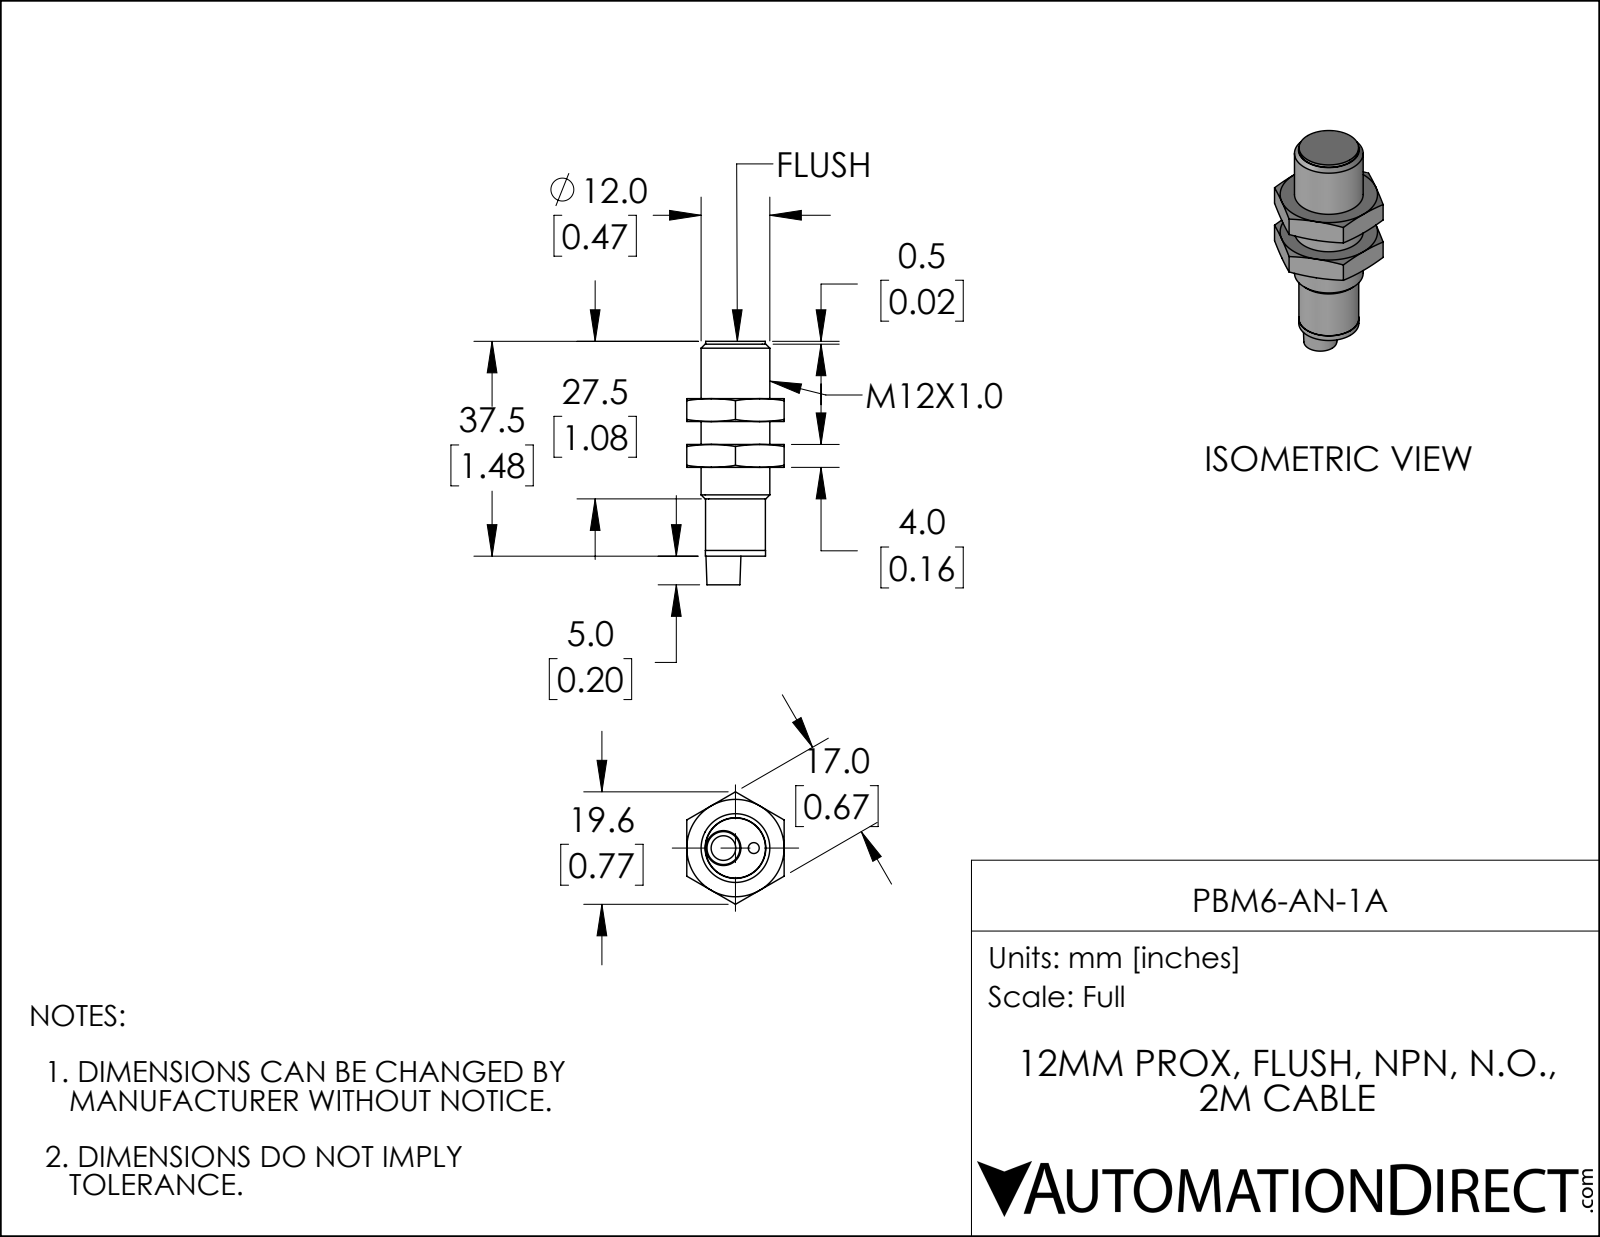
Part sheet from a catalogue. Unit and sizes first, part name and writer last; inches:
Units: inches
Overall size (bounding box): 1.673 × 0.472 × 0.472
Round holes (diameter × count): ⌀0.075 ×1, ⌀0.169 ×1
Round bosses / shafts (diameter × count): ⌀0.472 ×1, ⌀0.413 ×1, ⌀0.411 ×1, ⌀0.409 ×1
Main face-to-face distances: 1.476, 1.437, 0.039, 1.673, 0.236, 0.197, 0.02, 1.417, 1.457, 1.654
Hole centre spacings: 0.209
Volume: 0.243 in³ · Surface area: 2.689 in²
Bodies: 1 solid, 17 faces (8 planar, 6 cylindrical, 3 other)
Part name (STEP PRODUCT): DSD-0275
STEP written by: SolidWorks 2019 (AUTOMOTIVE_DESIGN)
